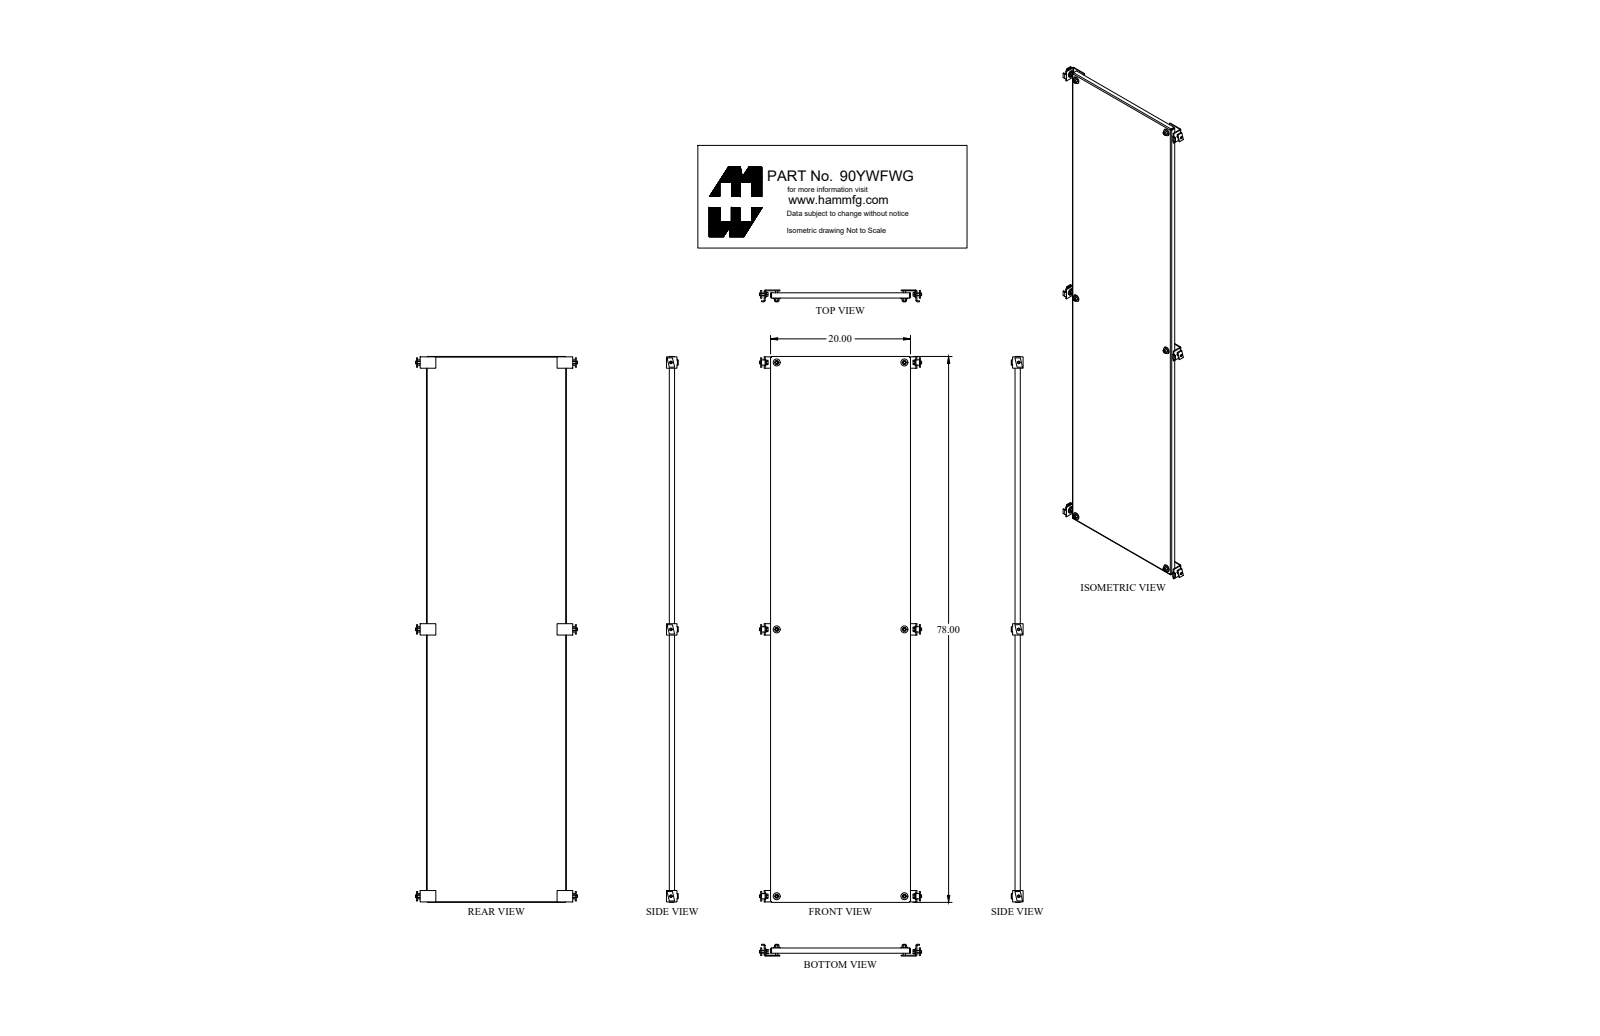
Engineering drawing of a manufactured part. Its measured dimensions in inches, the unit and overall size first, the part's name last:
Units: inches
Overall size (bounding box): 78 × 22.582 × 1.687
Round holes (diameter × count): ⌀0.563 ×6, ⌀0.437 ×3
Round bosses / shafts (diameter × count): ⌀0.65 ×6, ⌀0.375 ×6, ⌀0.33 ×6
Partial cylindrical surfaces — rounded edges, fillets, slot ends (radius × count): R0.048 ×4, R0.06 ×4, R0.143 ×4, R0.185 ×4
Main face-to-face distances: 0.095, 19.905, 19.81, 20, 0.125, 77.905, 1.032, 0.937, 1.157, 1.062
Hole centre spacings: 38.125, 42.268, 18.25, 76.25, 78.404, 38.13, 38.13, 76.26
Volume: 165 in³ · Surface area: 3 472 in²
Bodies: 13 solids, 270 faces (130 planar, 92 cylindrical, 48 other)
Part name (STEP PRODUCT): 90YWFWG_Default
STEP written by: SolidWorks 2018 (CONFIG_CONTROL_DESIGN)
